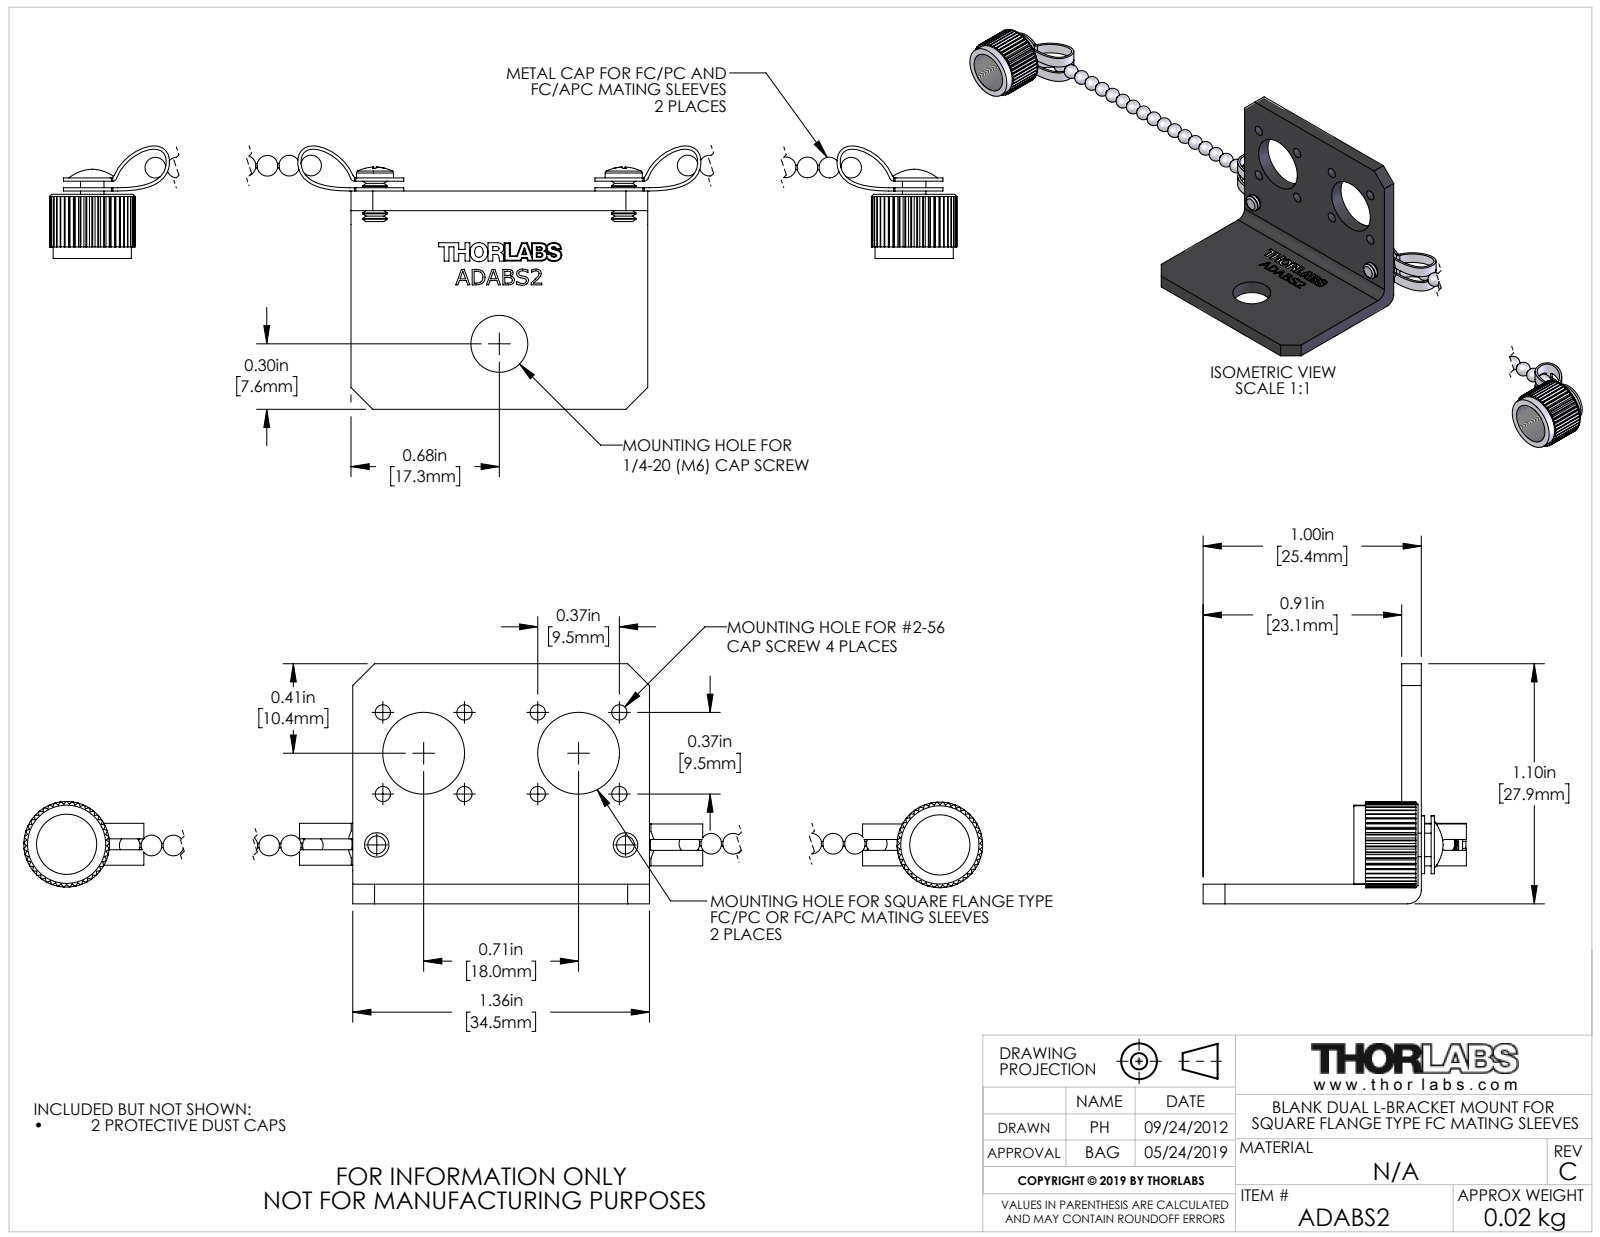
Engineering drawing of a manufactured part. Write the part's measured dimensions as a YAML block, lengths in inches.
part_name: "TTN004639-E0W"
step_written_by: "SolidWorks 2011 (AUTOMOTIVE_DESIGN)"
units: inches
bodies: {solids: 11, faces: 1029, planar: 529, cylindrical: 260, other: 240}
overall_size: [3.722, 1.557, 1.1]
volume: 0.275
surface_area: 10.11
round_holes:
  - {diameter: 0.07, count: 8}
  - {diameter: 0.162, count: 4}
  - {diameter: 0.089, count: 2}
  - {diameter: 0.276, count: 2}
  - {diameter: 0.261, count: 1}
  - {diameter: 0.375, count: 1}
  - {diameter: 0.375, count: 1}
round_bosses_or_shafts:
  - {diameter: 0.359, count: 2}
  - {diameter: 0.17, count: 2}
  - {diameter: 0.112, count: 2}
  - {diameter: 0.107, count: 2}
  - {diameter: 0.02, count: 2}
partial_cylinders:
  - {radius: 0.009, count: 40}
  - {radius: 0.02, count: 8}
  - {radius: 0.132, count: 4}
  - {radius: 0.063, count: 2}
  - {radius: 0.196, count: 2}
face_to_face_distances: [0.09, 0.015, 0.045, 0.06, 0.03, 1.36, 0.075, 0.044, 0.119, 1.01]
hole_center_spacings: [0.265, 0.374, 0.71, 0.529, 0.556, 0.803, 0.917, 0.235]
